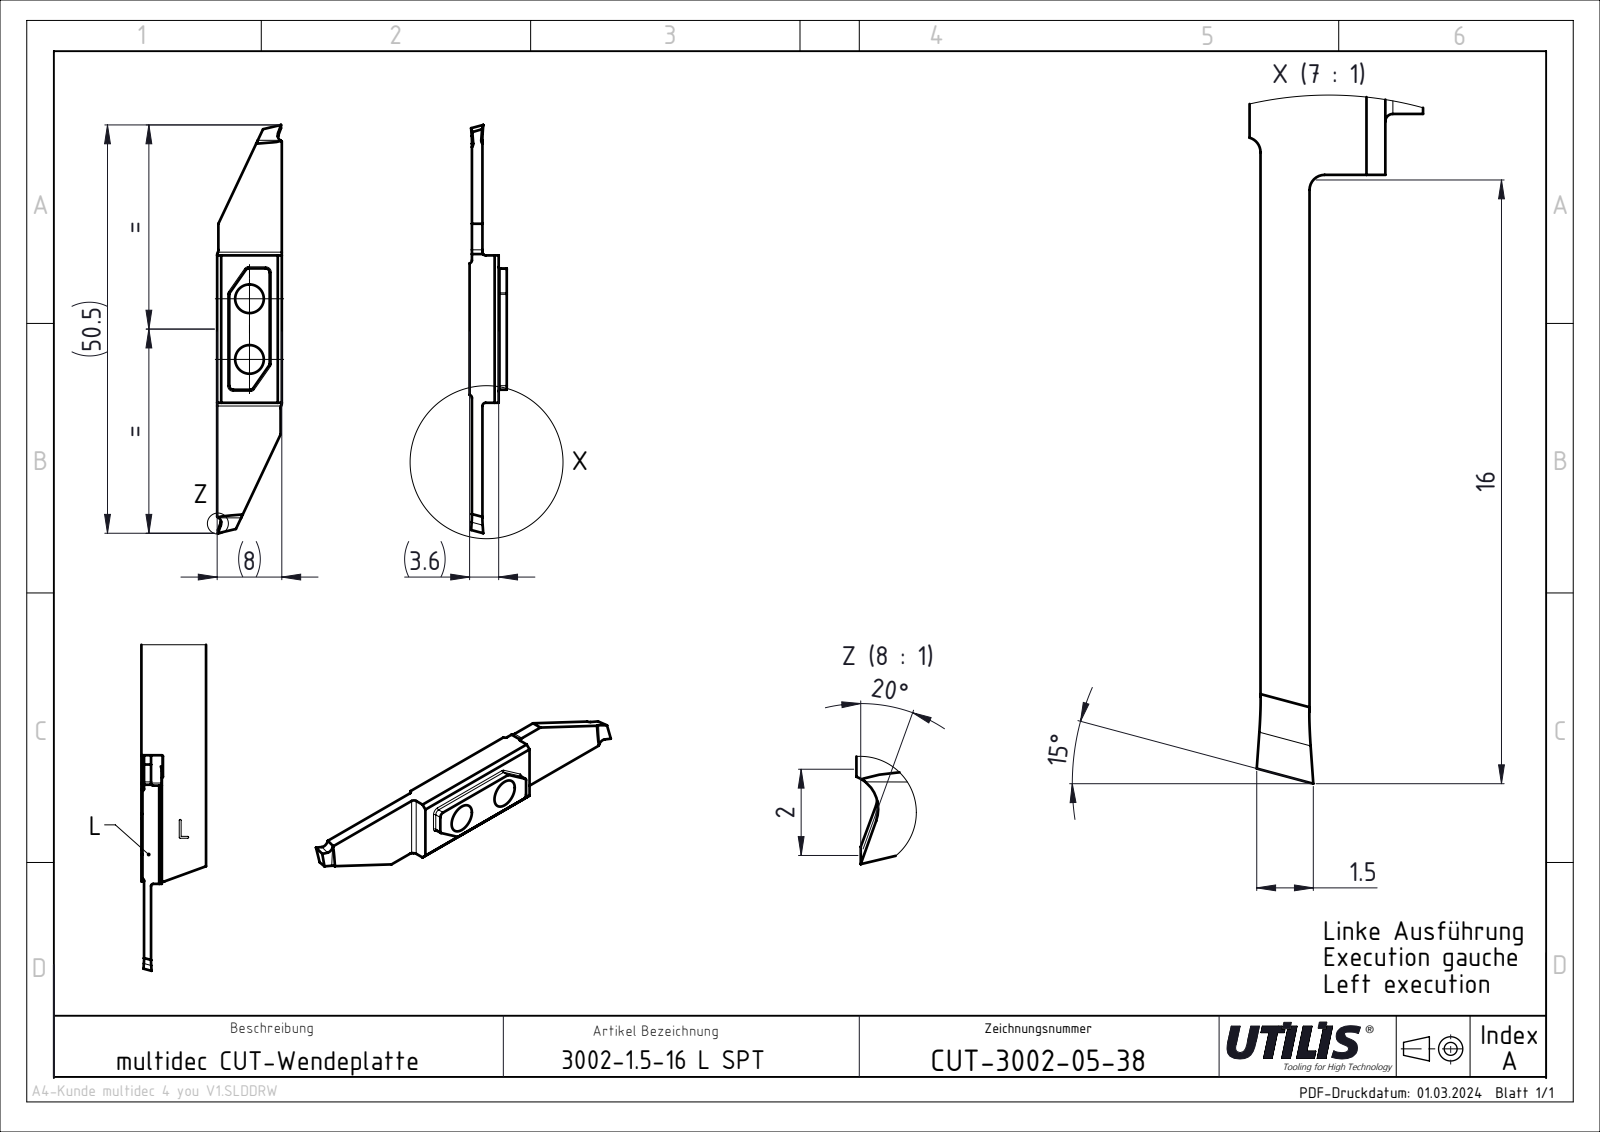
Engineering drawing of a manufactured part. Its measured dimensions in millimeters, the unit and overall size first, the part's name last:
Units: millimetres
Overall size (bounding box): 50.5 × 8 × 3.6
Round holes (diameter × count): ⌀3.55 ×2
Partial cylindrical surfaces — rounded edges, fillets, slot ends (radius × count): R0.4 ×4, R1 ×2
Main face-to-face distances: 1.3, 1.59, 3.6, 3.31, 2.01, 8, 18.09, 18.22, 1.11, 7.85
Hole centre spacings: 7.5
Volume: 683 mm³ · Surface area: 941 mm²
Bodies: 1 solid, 32 faces (22 planar, 10 cylindrical, 0 other)
Part name (STEP PRODUCT): CUT-3002 SPT Slim_and_Deep; ASME Y14.5
STEP written by: SolidWorks 2023 SP4 || FormatWorks Professional (AP242_MANAGED_MODEL_BASED_3D_ENGINEERING_MIM_LF)
